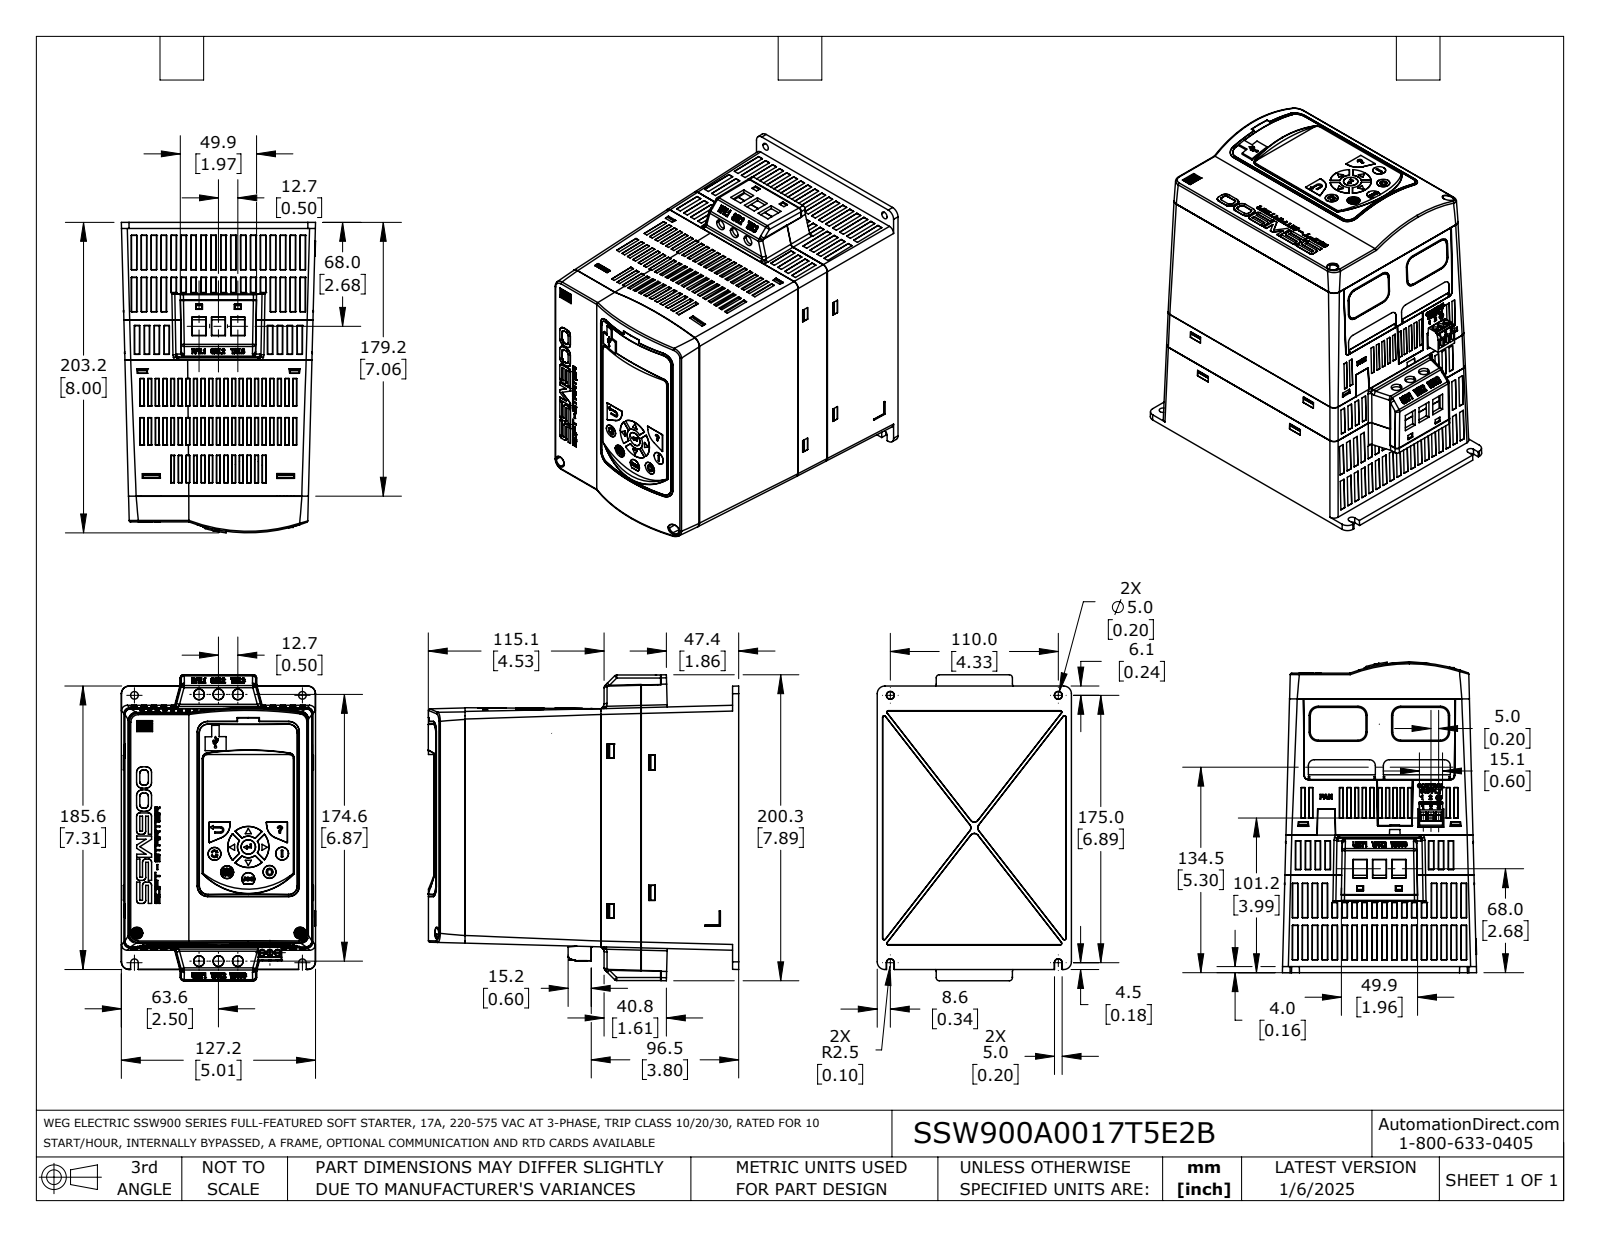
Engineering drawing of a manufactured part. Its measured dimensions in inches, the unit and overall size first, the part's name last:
Units: inches
Overall size (bounding box): 8.002 × 7.885 × 5.006
Round holes (diameter × count): ⌀0.118 ×3, ⌀0.165 ×3, ⌀0.133 ×1, ⌀0.287 ×1
Round bosses / shafts (diameter × count): ⌀0.15 ×3, ⌀0.087 ×2, ⌀0.151 ×1, ⌀0.057 ×1, ⌀0.034 ×1
Partial cylindrical surfaces — rounded edges, fillets, slot ends (radius × count): R0.079 ×42, R0.02 ×19, R0.039 ×17, R0.012 ×14, R0.008 ×8, R0.15 ×8, R0.157 ×8, R0.006 ×7
Main face-to-face distances: 4.466, 0.325, 5.776, 0.15, 0.149, 0.149, 7.811, 7.487, 0.055, 0.333
Hole centre spacings: 0.197, 0.199, 0.394, 0.398, 0.565, 0.601, 0.693, 0.768
Volume: 41.94 in³ · Surface area: 551 in²
Bodies: 3 solids, 4554 faces (3611 planar, 239 cylindrical, 704 other)
Part name (STEP PRODUCT): SSW900A0017T5E2B
STEP written by: SolidWorks 2021 (AUTOMOTIVE_DESIGN)
